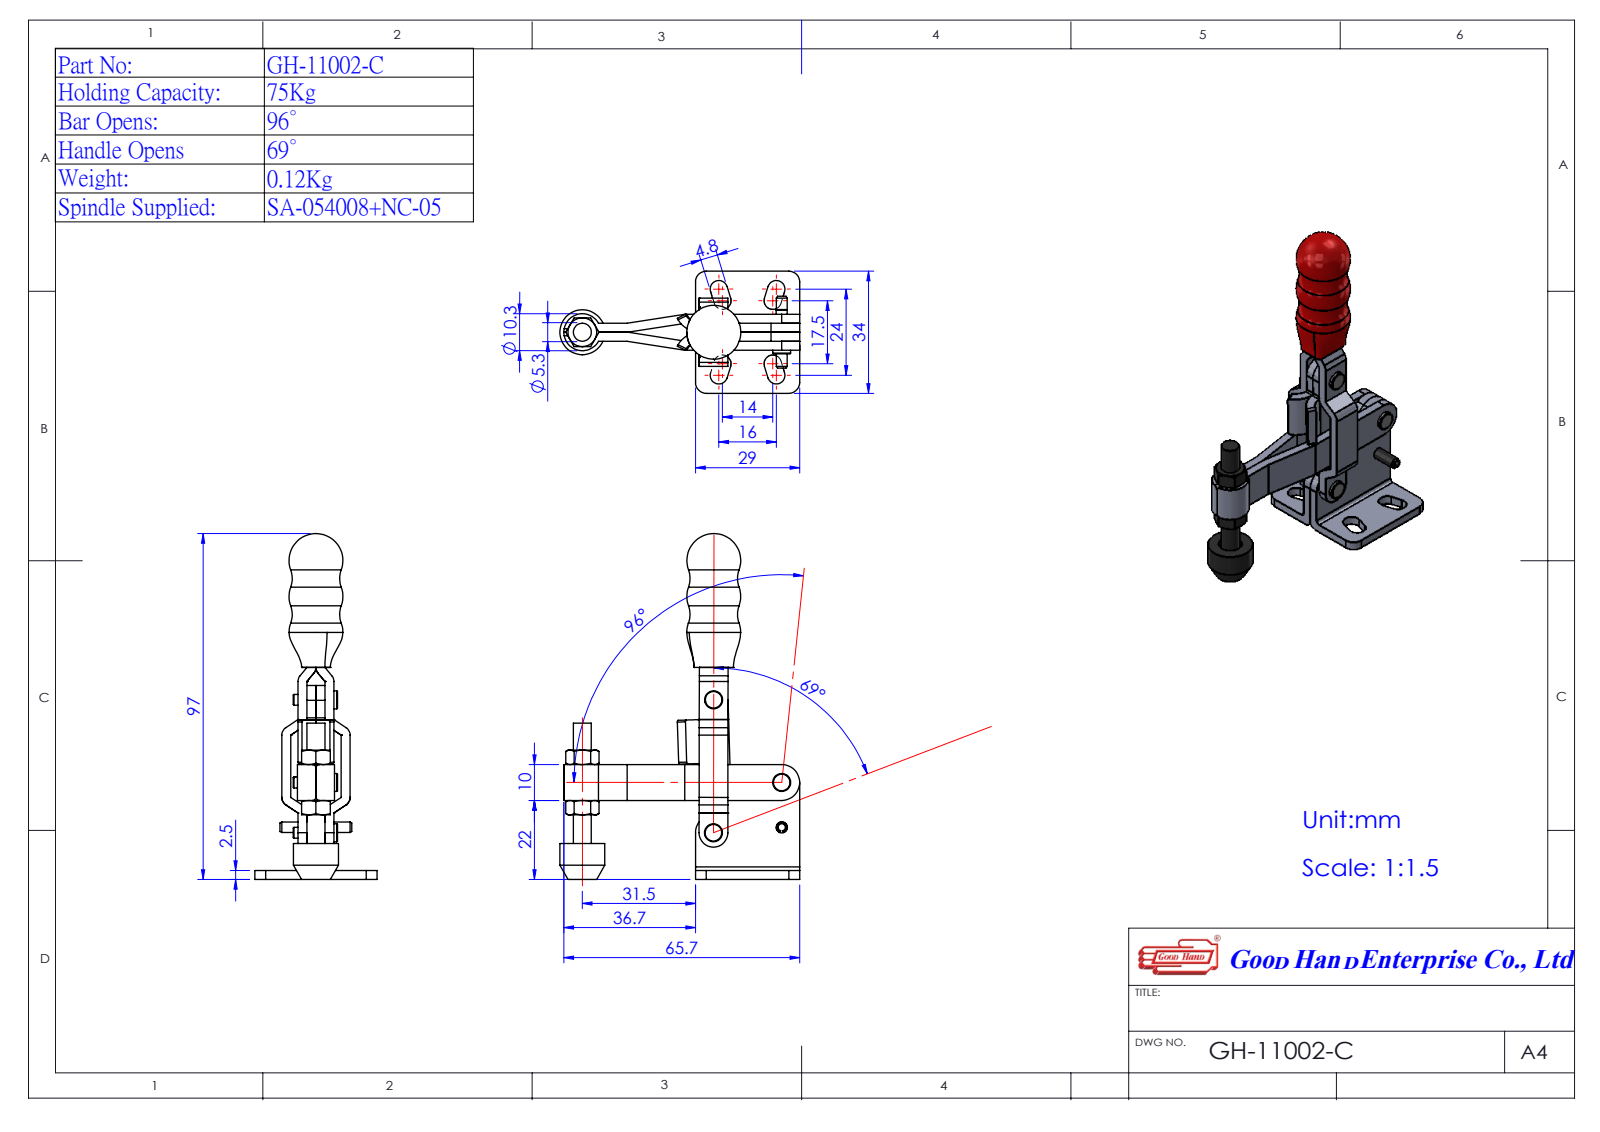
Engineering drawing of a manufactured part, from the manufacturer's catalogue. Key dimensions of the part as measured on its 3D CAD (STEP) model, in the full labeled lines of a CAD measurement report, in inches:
Part name (STEP PRODUCT): Group2^GH-11002-C(簡化); 零件82^GH-11002-C(簡化); Group3^GH-11002-C(簡化); Group5^GH-11002-C(簡化) (+2 more)
STEP written by: SolidWorks 2016 (AUTOMOTIVE_DESIGN)
Units: inches
Bodies: 6 solids, 274 faces (114 planar, 98 cylindrical, 62 other)
Overall size (bounding box): 3.819 × 2.628 × 1.339
Volume: 1.171 in³ · Surface area: 23.05 in²
Round holes (diameter × count): ⌀0.098 ×4, ⌀0.165 ×1, ⌀0.197 ×1, ⌀0.209 ×1, ⌀0.354 ×1
Round bosses / shafts (diameter × count): ⌀0.197 ×4, ⌀0.157 ×2, ⌀0.492 ×1, ⌀0.406 ×1, ⌀0.122 ×1
Partial cylindrical surfaces — rounded edges, fillets, slot ends (radius × count): R0.094 ×8, R0.02 ×4, R0.118 ×4, R0.157 ×3, R0.039 ×2, R0.079 ×2, R0.098 ×2, R0.177 ×2
Main face-to-face distances: 0.098, 0.197, 0.295, 0.394, 0.472, 0.276, 0.177, 0.374, 0.571, 0.768
Hole centre spacings: 0.552, 0.719, 0.906, 0.929, 1.173, 1.457
